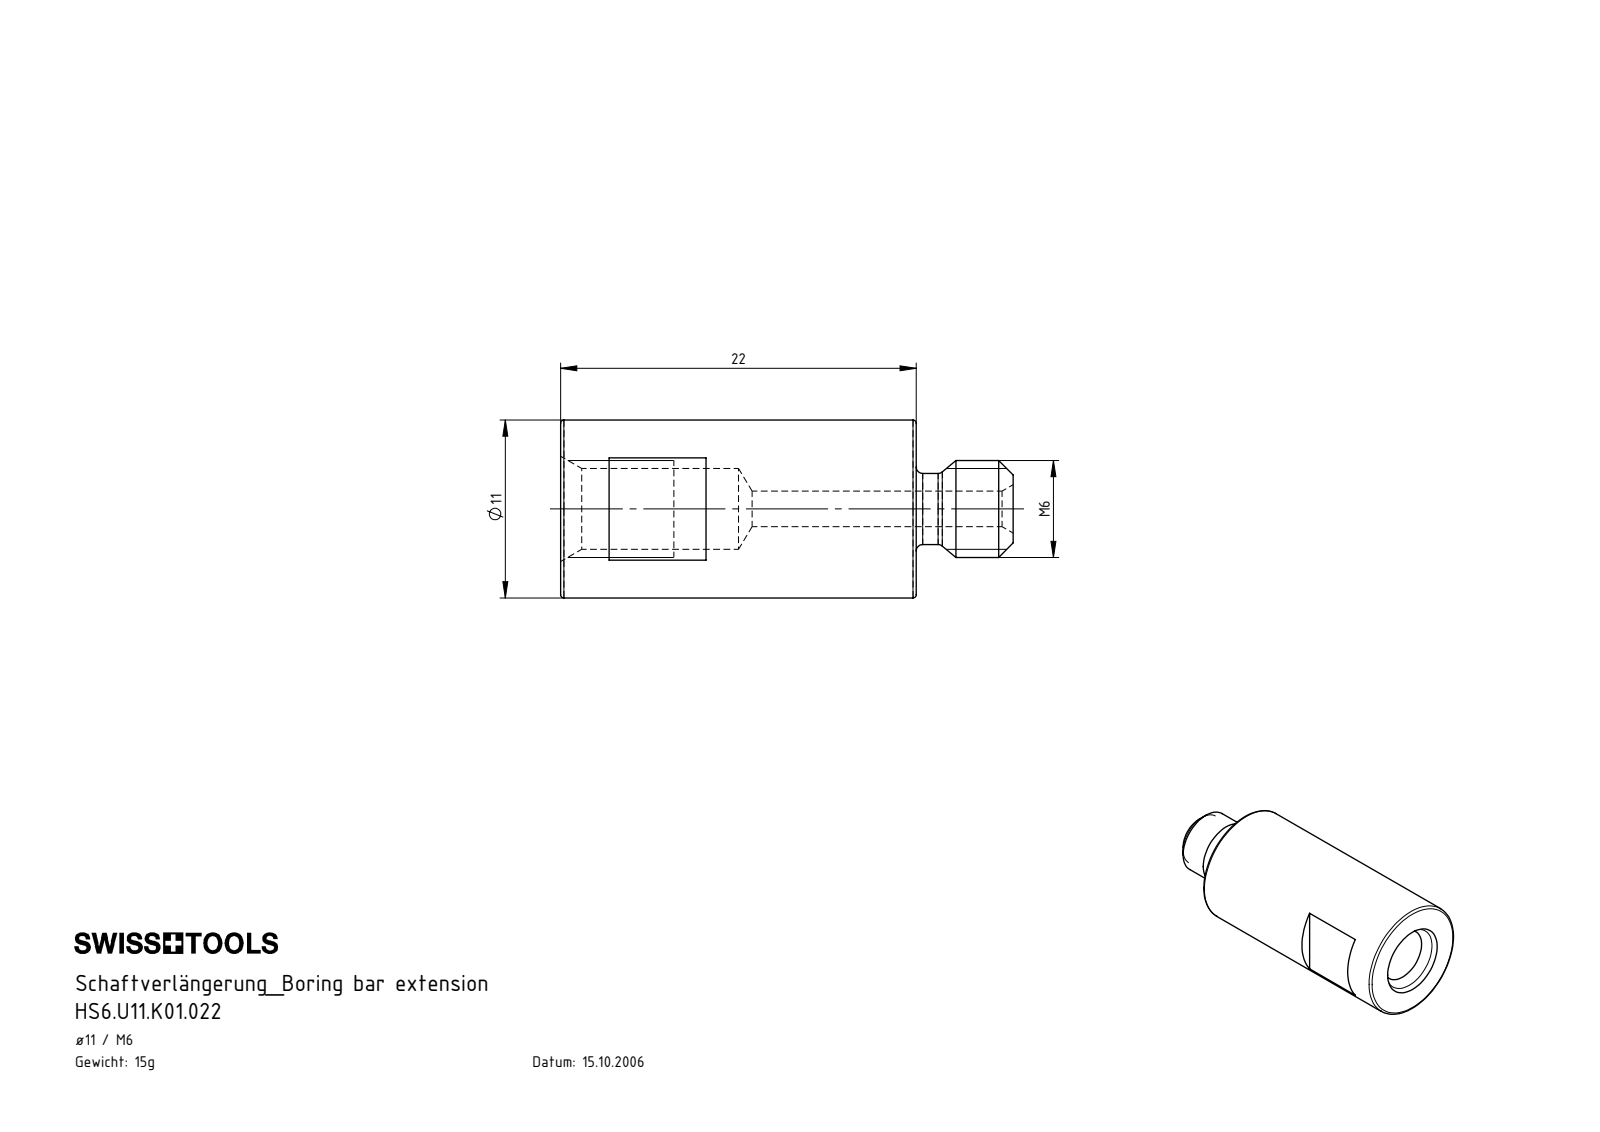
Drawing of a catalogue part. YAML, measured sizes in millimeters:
part_name: "HS6.U11.K01.022"
step_written_by: "SolidWorks 2022 (CONFIG_CONTROL_DESIGN)"
units: millimeters
bodies: {solids: 1, faces: 37, planar: 9, cylindrical: 10, other: 18}
overall_size: [28, 11, 11]
volume: 1880
surface_area: 1335
round_holes:
  - {diameter: 2.2, count: 1}
  - {diameter: 5, count: 1}
round_bosses_or_shafts:
  - {diameter: 11, count: 1}
  - {diameter: 6, count: 1}
  - {diameter: 4.4, count: 1}
face_to_face_distances: [22, 9, 19, 6, 3, 13, 25, 28]
